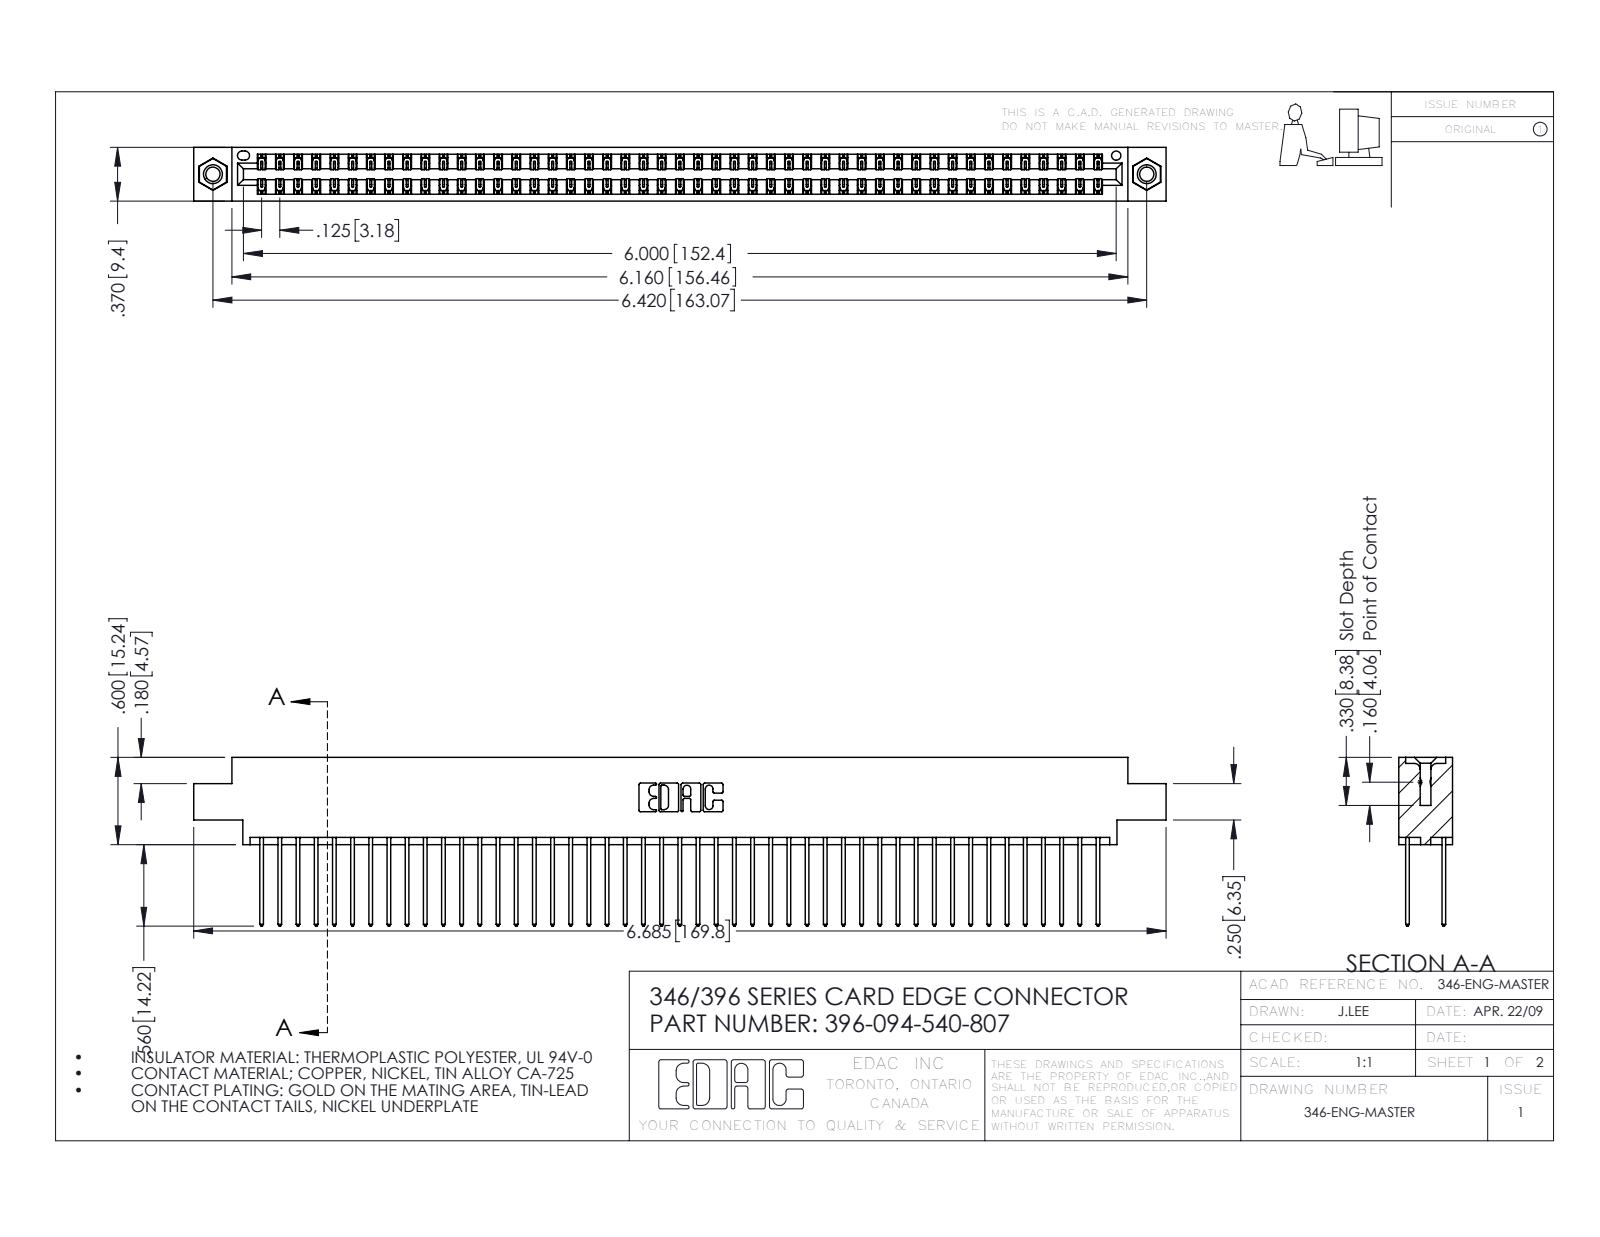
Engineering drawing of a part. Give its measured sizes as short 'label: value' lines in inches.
name: 345-250-001_345-250-005-103; 396-094-540-807; 345-292-001_345-293-140; 346 Part_0.170 Offset - 0.156 Dia-TI
written by: SolidWorks 2016 (CONFIG_CONTROL_DESIGN)
unit: in
bodies: 97 solids, 5074 faces (3402 planar, 1656 cylindrical, 16 other)
size: 6.685 × 1.16 × 0.37
volume: 1.024 in³; area: 38.83 in²
holes: 2× ⌀0.098, 2× ⌀0.125, 2× ⌀0.156, 1× ⌀0.064
bosses: 2× ⌀0.155
rounds: 141× R0.006, 94× R0.01, 22× R0.01, 6× R0.007, 6× R0.031, 3× R0.026, 2× R0.014, 2× R0.022
face distances: 0.048, 0.322, 0.25, 0.072, 0.298, 0.025, 0.37, 0.275, 0.222, 0.148
hole spacings: 0.246, 6.211, 6.42
